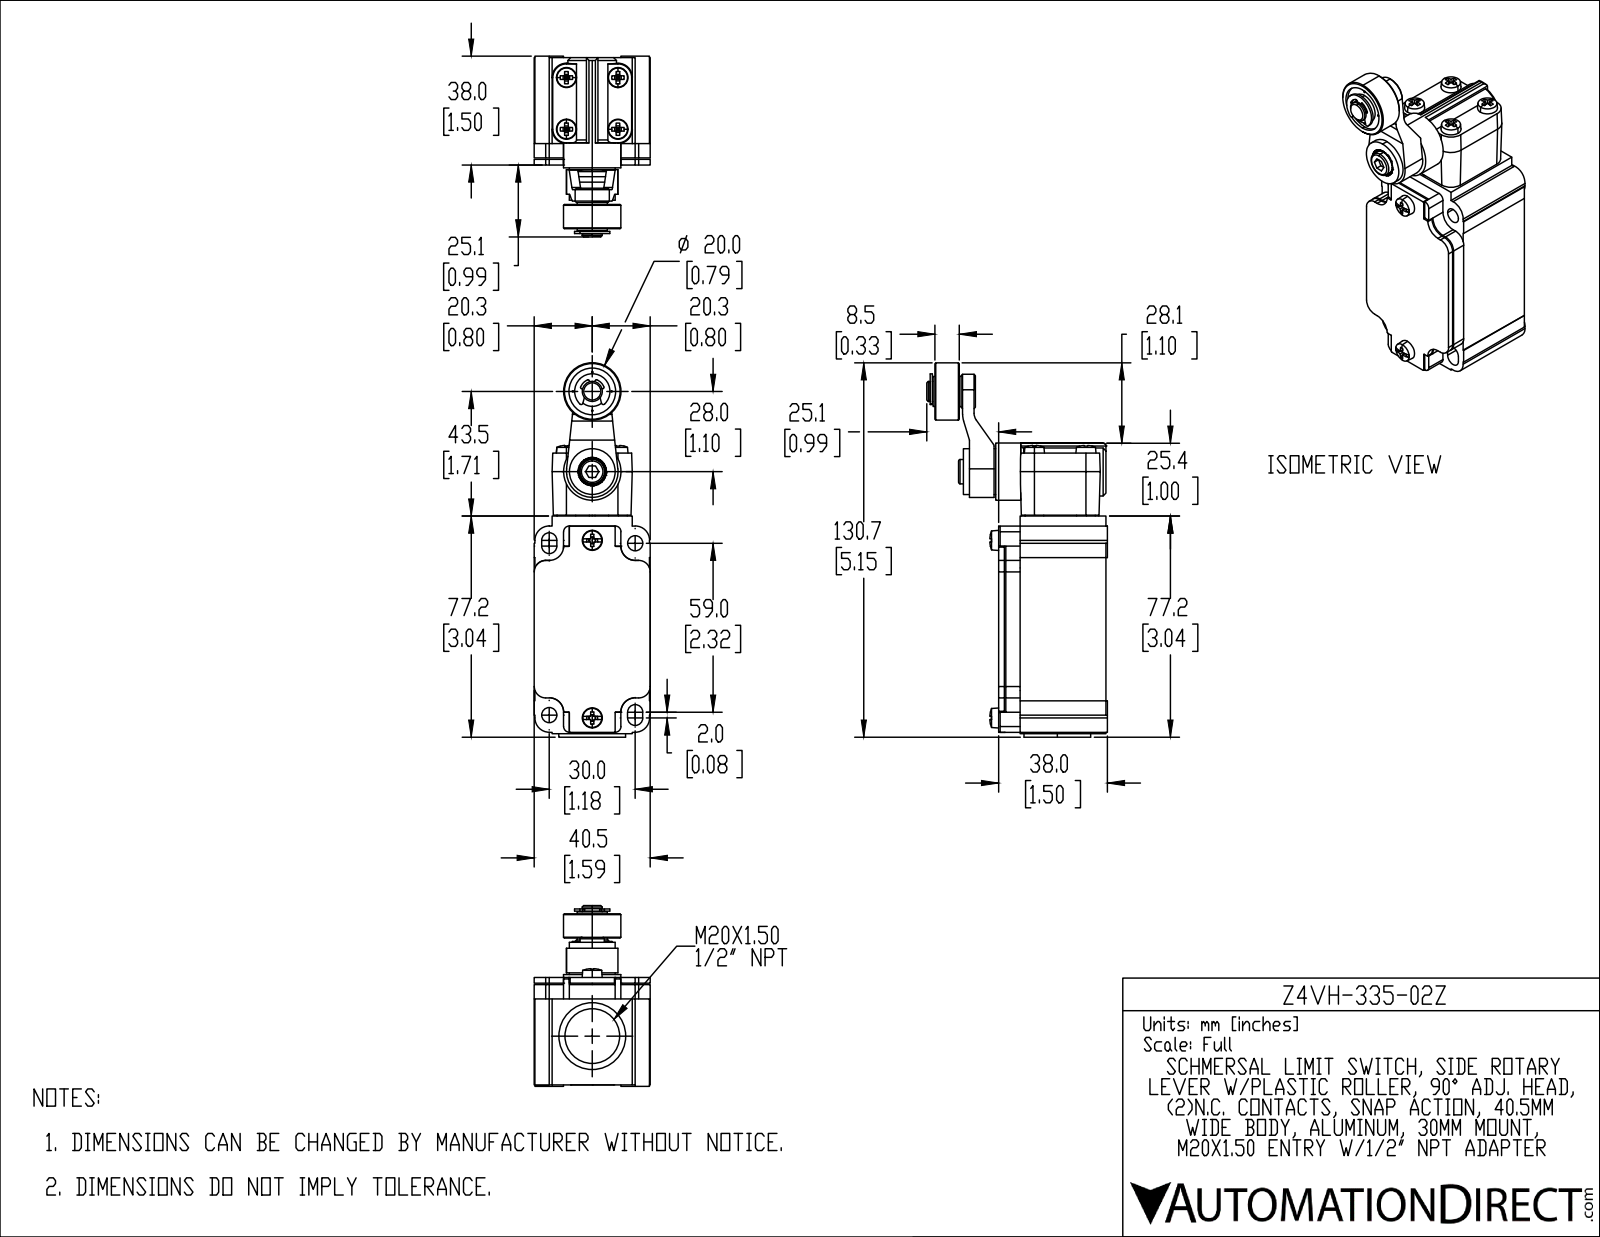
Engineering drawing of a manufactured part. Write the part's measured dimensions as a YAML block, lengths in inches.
part_name: "Z4VH-335-02Z"
step_written_by: "SolidWorks 2019 (AUTOMOTIVE_DESIGN)"
units: inches
bodies: {solids: 1, faces: 1021, planar: 613, cylindrical: 299, other: 109}
overall_size: [5.146, 2.484, 1.594]
volume: 7.893
surface_area: 45.74
round_holes:
  - {diameter: 0.02, count: 4}
  - {diameter: 0.209, count: 2}
  - {diameter: 0.224, count: 1}
  - {diameter: 0.642, count: 1}
  - {diameter: 0.75, count: 1}
round_bosses_or_shafts:
  - {diameter: 0.787, count: 2}
  - {diameter: 0.079, count: 2}
  - {diameter: 0.917, count: 1}
  - {diameter: 0.709, count: 1}
  - {diameter: 0.669, count: 1}
  - {diameter: 0.63, count: 1}
  - {diameter: 0.413, count: 1}
  - {diameter: 0.335, count: 1}
partial_cylinders:
  - {radius: 0.008, count: 72}
  - {radius: 0.006, count: 36}
  - {radius: 0.1, count: 16}
  - {radius: 0.157, count: 13}
  - {radius: 0.01, count: 12}
  - {radius: 0.197, count: 12}
  - {radius: 0.079, count: 4}
  - {radius: 0.104, count: 4}
face_to_face_distances: [0.02, 1.398, 0.079, 1.378, 1.476, 0.098, 1.181, 0.295, 1.594, 0.197]
hole_center_spacings: [0.266, 0.376, 0.531, 1.914, 2.112, 2.169, 2.256, 2.425]
